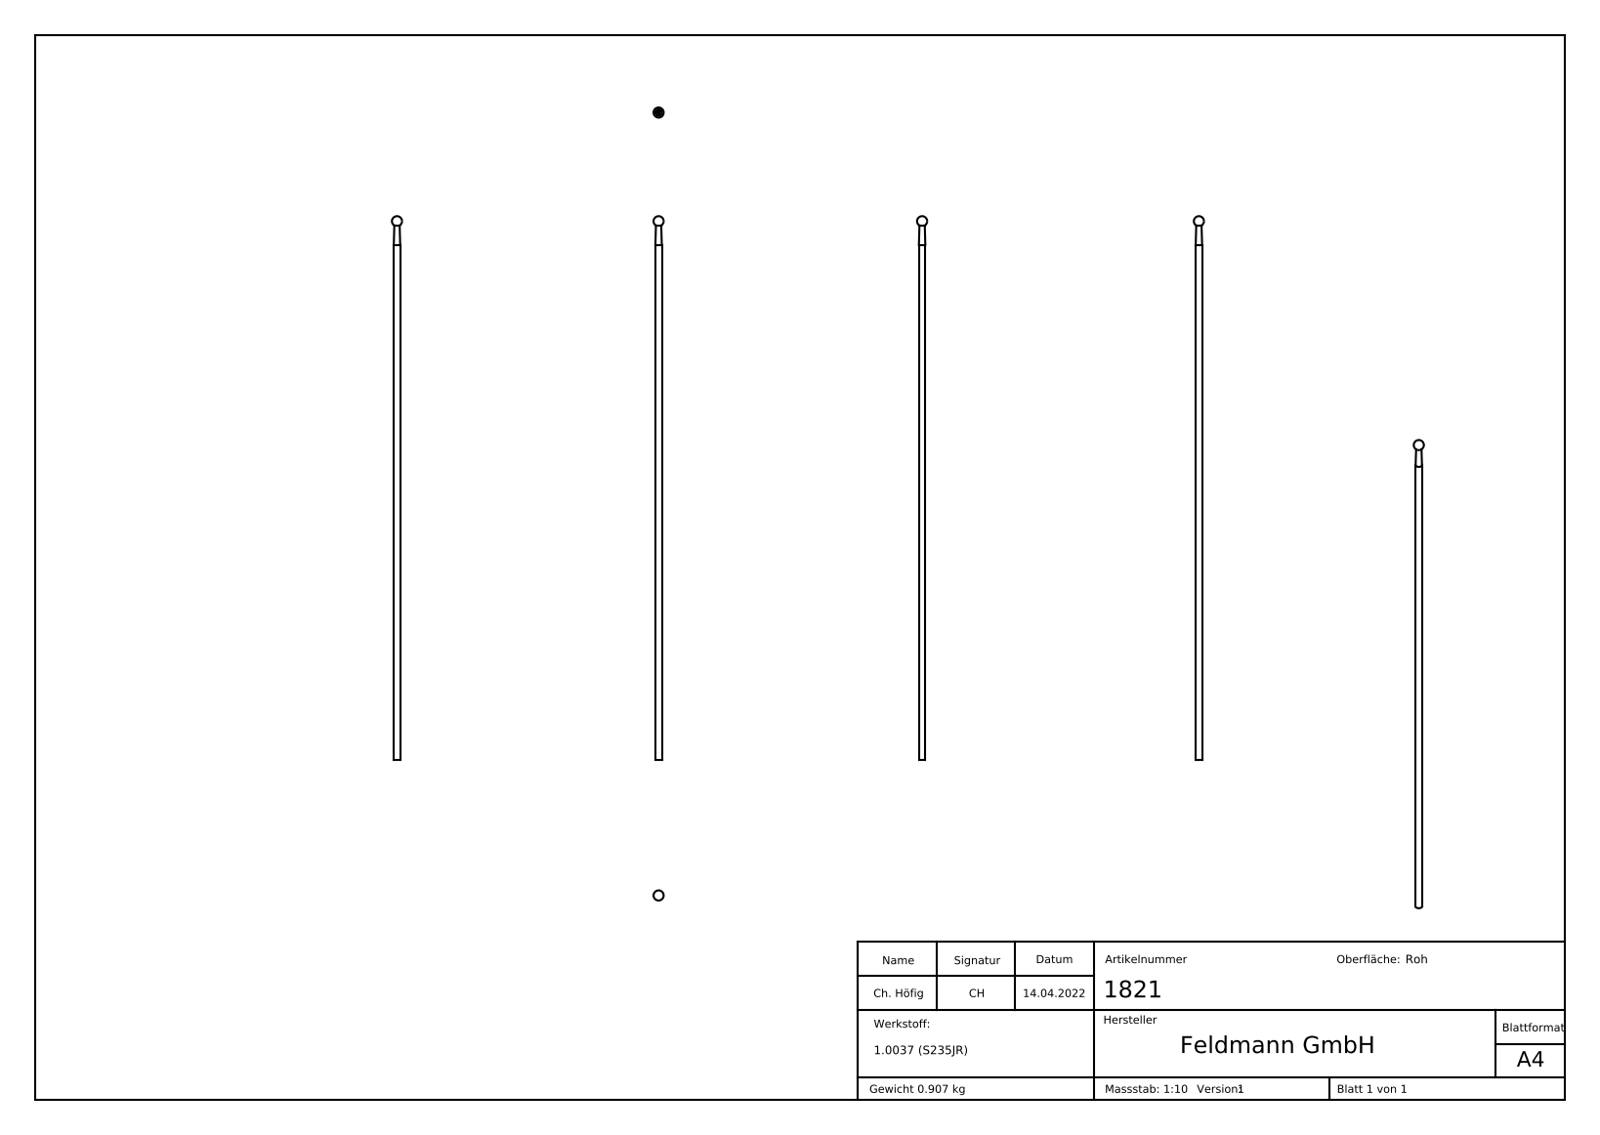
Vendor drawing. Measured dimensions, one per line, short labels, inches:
name: 1821
written by: SolidWorks 2018 (CONFIG_CONTROL_DESIGN)
unit: in
bodies: 1 solid, 207 faces (113 planar, 1 cylindrical, 93 other)
size: 40.157 × 0.748 × 0.748
volume: 7.095 in³; area: 60.21 in²
bosses: 1× ⌀0.472
face distances: 0.069, 0.089, 0.091, 0.077, 0.019, 0.091, 0.019, 0.059, 0.064, 0.016
